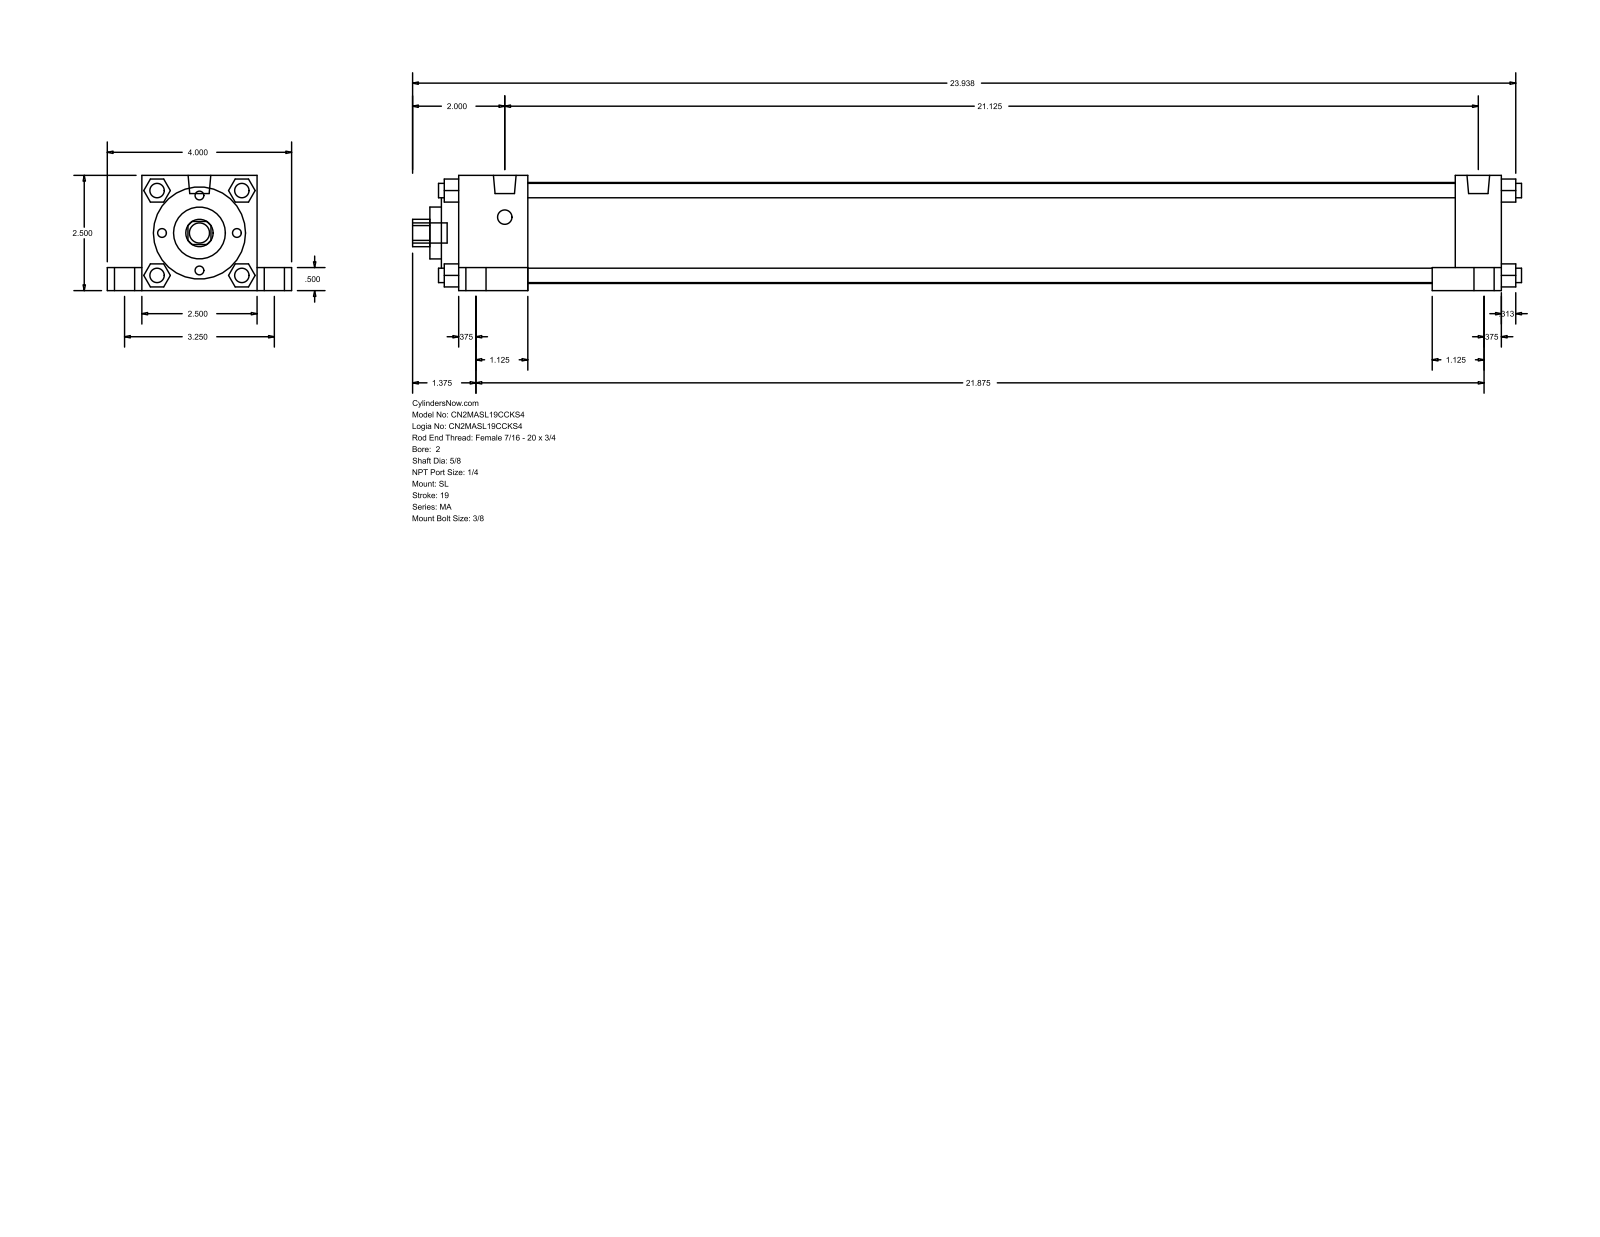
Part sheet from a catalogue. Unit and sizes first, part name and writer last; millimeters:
Units: millimetres
Overall size (bounding box): 611.19 × 101.6 × 63.5
Round holes (diameter × count): ⌀15.88 ×1, ⌀28.57 ×1, ⌀50.8 ×1, ⌀55.63 ×1
Round bosses / shafts (diameter × count): ⌀7.94 ×8, ⌀11.11 ×5, ⌀17.46 ×4, ⌀12.49 ×2
Partial cylindrical surfaces — rounded edges, fillets, slot ends (radius × count): R7.54 ×1
Main face-to-face distances: 63.5, 12.7, 9.52, 511.17, 19.05, 82.55, 38.1, 50.8, 574.68, 536.58
Bodies: 0 solids, 150 faces (113 planar, 37 cylindrical, 0 other)
Part name (STEP PRODUCT): MA_SL__0200_0.625
STEP written by: GSSL Pune (CONFIG_CONTROL_DESIGN)
